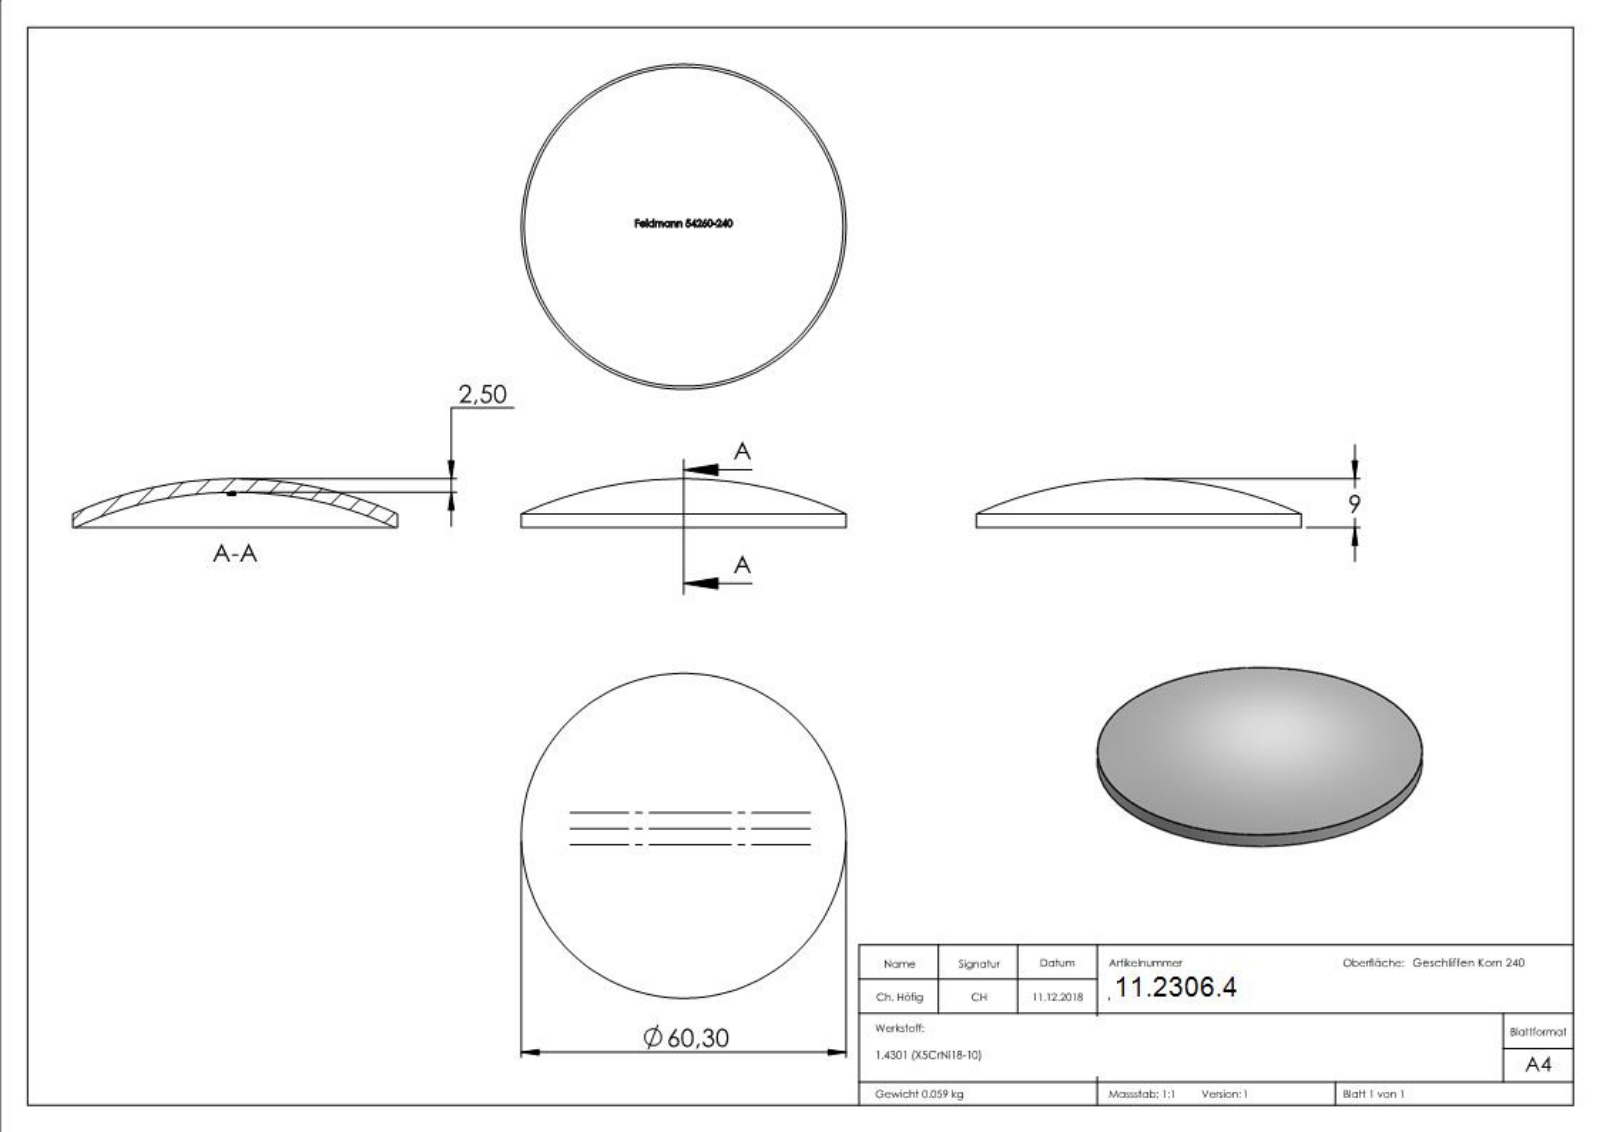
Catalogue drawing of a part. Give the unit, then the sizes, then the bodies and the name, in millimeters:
Units: millimetres
Overall size (bounding box): 60.3 × 60.3 × 9
Round bosses / shafts (diameter × count): ⌀60.3 ×1
Main face-to-face distances: 0.44, 2.97, 0.39, 4.7, 1.32, 0.88, 14.62, 7.67, 10.94, 1.26
Volume: 7 471 mm³ · Surface area: 6 460 mm²
Bodies: 1 solid, 245 faces (106 planar, 2 cylindrical, 137 other)
Part name (STEP PRODUCT): 54260-240
STEP written by: SolidWorks 2015 (CONFIG_CONTROL_DESIGN)
